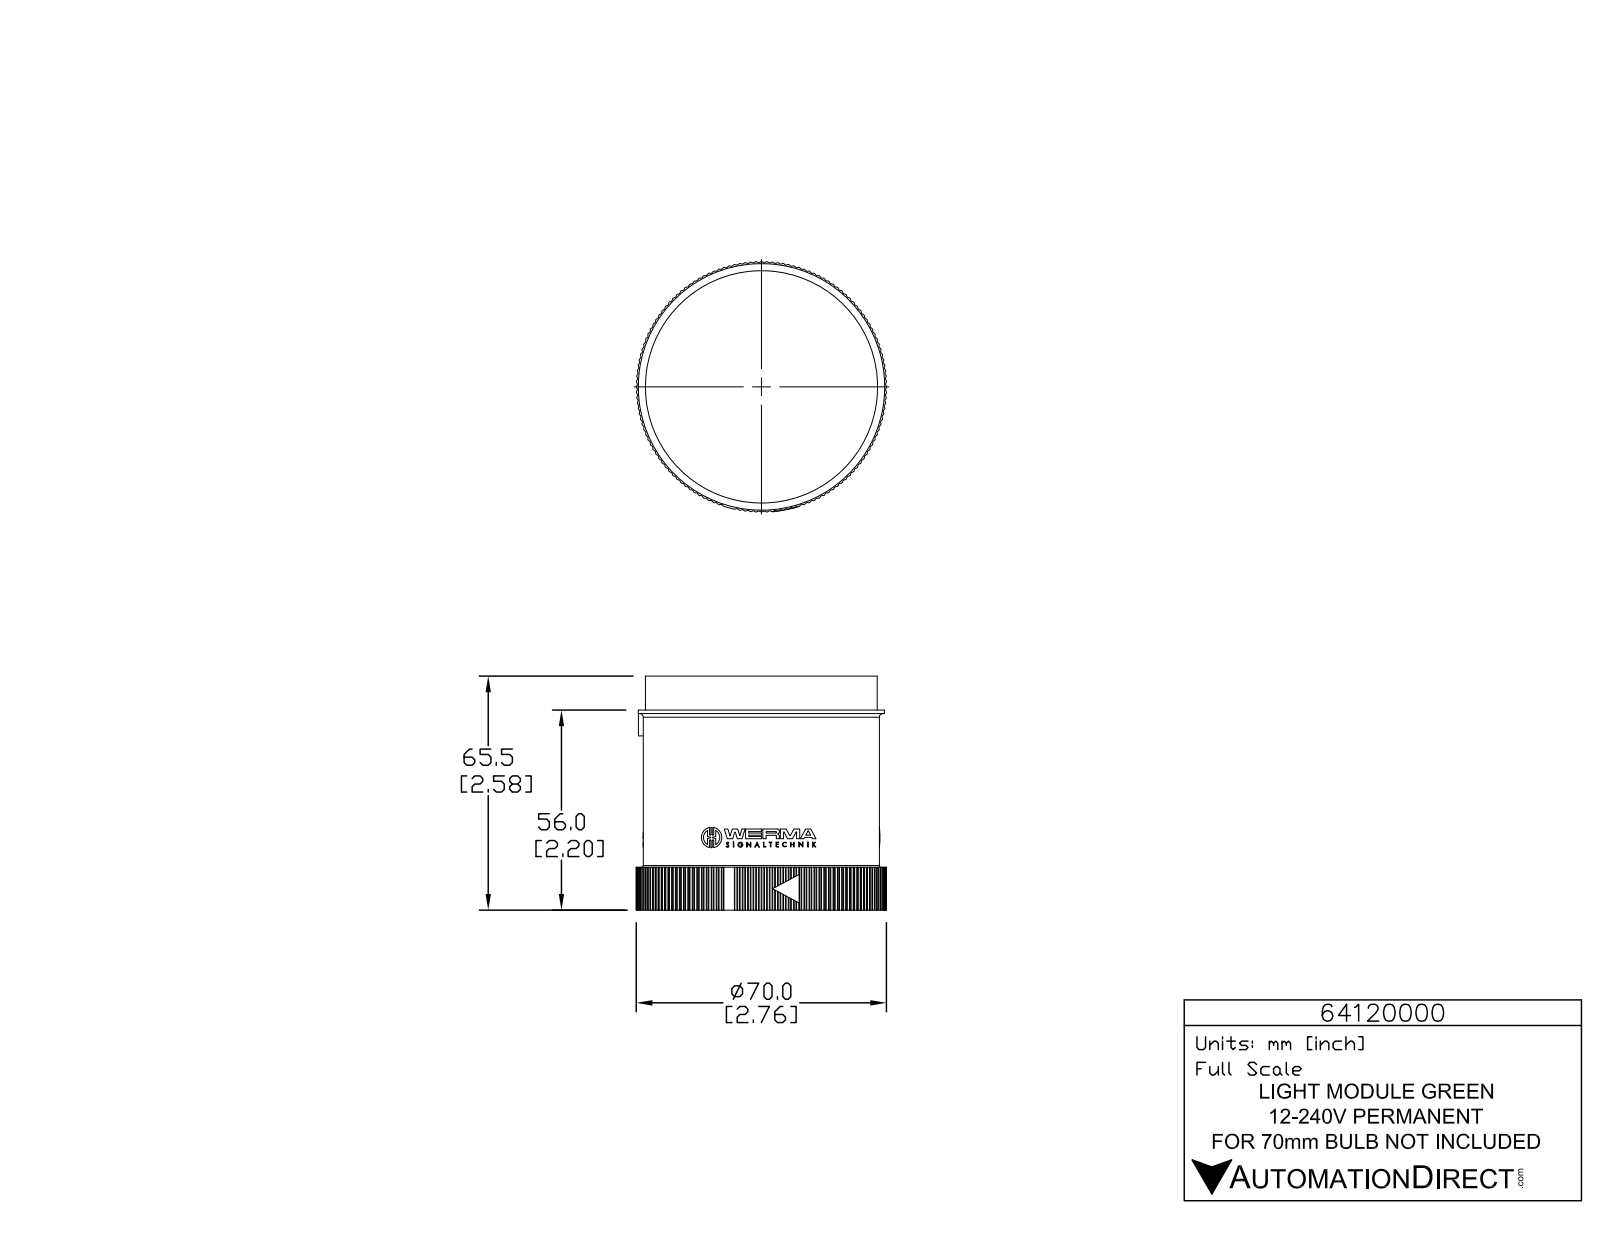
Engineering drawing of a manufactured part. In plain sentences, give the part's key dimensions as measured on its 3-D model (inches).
The part is named "64120000". Its 3-D file was written by "SolidWorks 2015 (AUTOMOTIVE_DESIGN)". It is 1 solid with 1400 faces: 832 planar, 563 cylindrical and 5 other. Overall it measures 2.762 by 2.762 by 2.579 inches. Its volume is 12.02 cubic inches and its surface area 37.48 square inches. Round holes: 3 of diameter 0.039, 1 of diameter 2.575. Round bosses or shafts: 3 of diameter 0.226, 3 of diameter 0.056, 1 of diameter 2.717, 1 of diameter 2.606, 1 of diameter 2.559. Partial cylindrical surfaces (rounded edges, fillets, slot ends): 285 of radius 0.008, 6 of radius 0.008, 6 of radius 0.008, 6 of radius 0.008, 6 of radius 0.131, 3 of radius 0.004, 3 of radius 0.005, 3 of radius 0.008. The main face-to-face distances are 2.201, 2.451, 0.378, 2.579, 2.205, 1.827, 0.374, 2.452, 0.472, 0.094.
